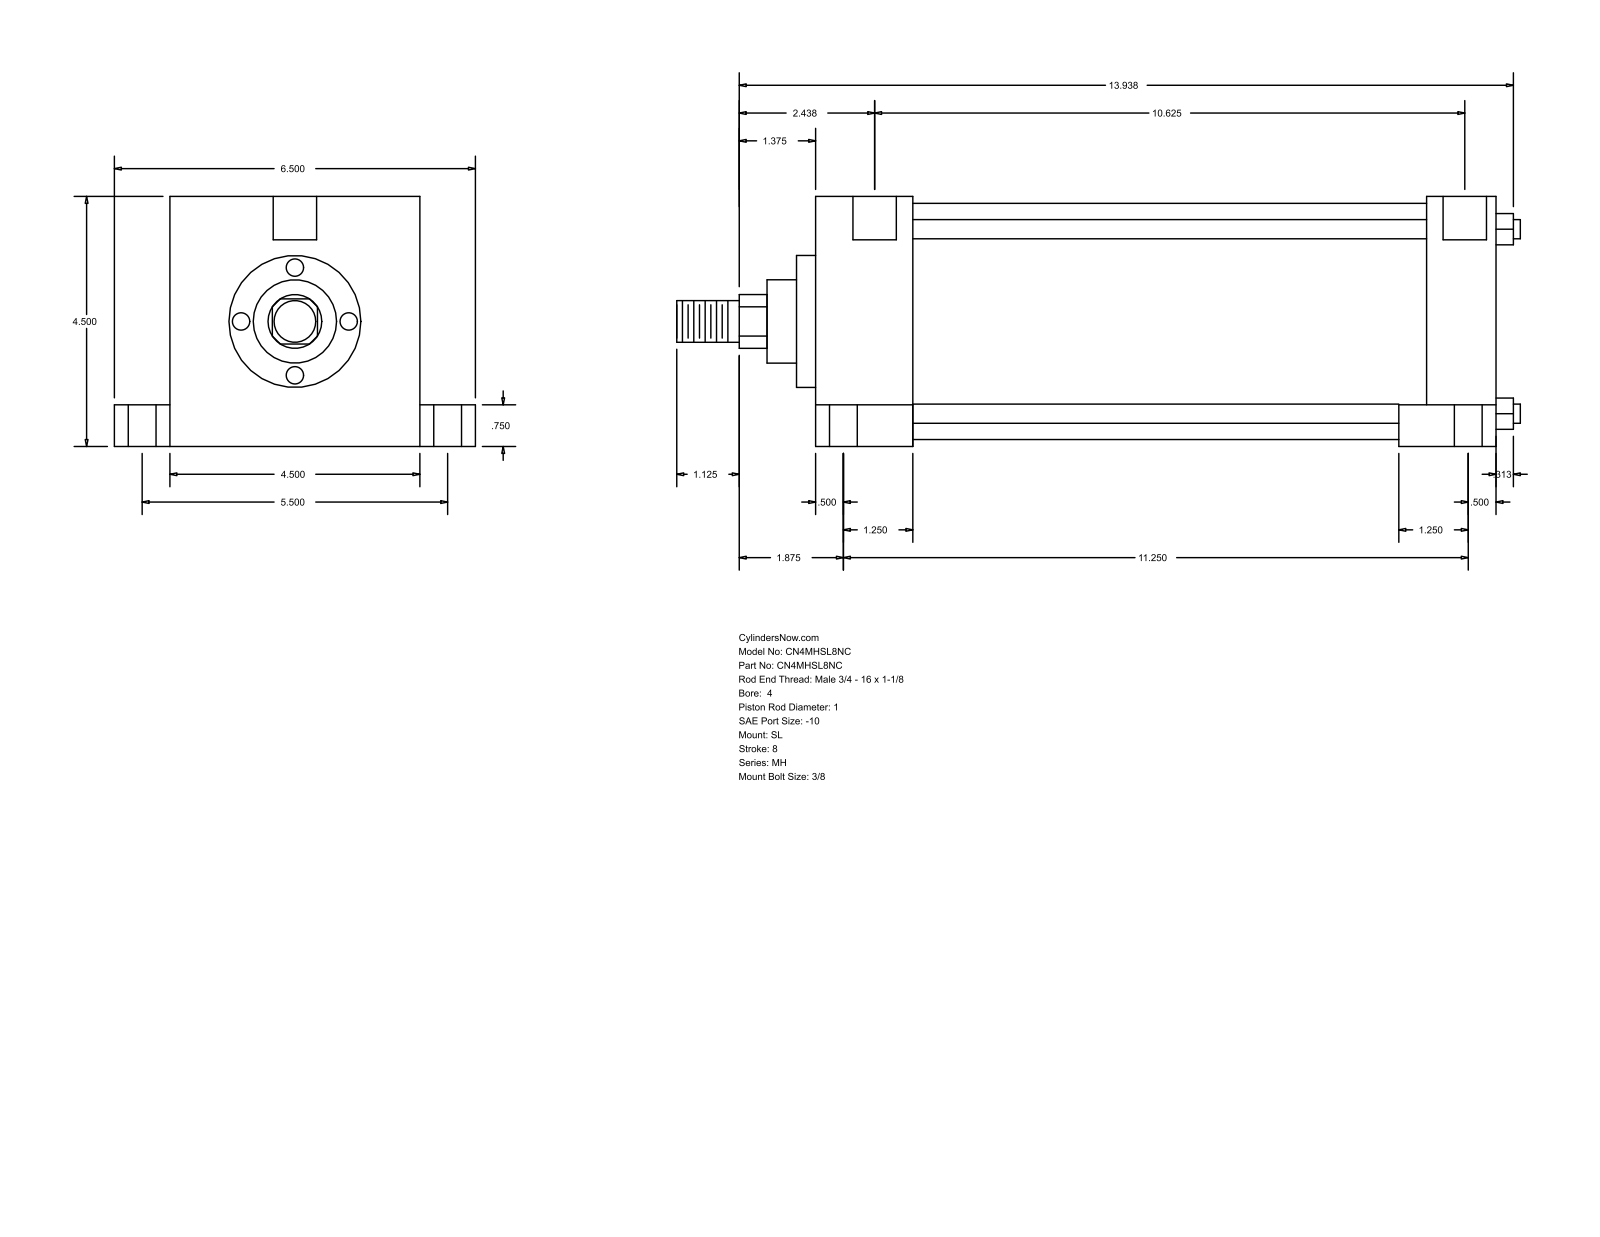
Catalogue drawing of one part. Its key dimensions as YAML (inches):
part_name: "MH_SL__0400_1"
step_written_by: "GSSL Pune (CONFIG_CONTROL_DESIGN)"
units: inches
bodies: {solids: 0, faces: 110, planar: 77, cylindrical: 33, other: 0}
overall_size: [15.187, 6.5, 4.5]
round_holes:
  - {diameter: 0.344, count: 4}
  - {diameter: 0.5, count: 4}
  - {diameter: 0.75, count: 4}
  - {diameter: 0.781, count: 2}
round_bosses_or_shafts:
  - {diameter: 0.345, count: 4}
  - {diameter: 4.25, count: 1}
  - {diameter: 2.375, count: 1}
  - {diameter: 1.5, count: 1}
  - {diameter: 1, count: 1}
  - {diameter: 0.75, count: 1}
partial_cylinders:
  - {radius: 0.484, count: 1}
face_to_face_distances: [4.5, 12.25, 1.75, 10.5, 11, 9.25, 1.25, 1, 5.5, 0.75]
hole_center_spacings: [2.75, 2.751, 2.795, 2.807, 5.5, 10.75, 11.036, 11.096]
